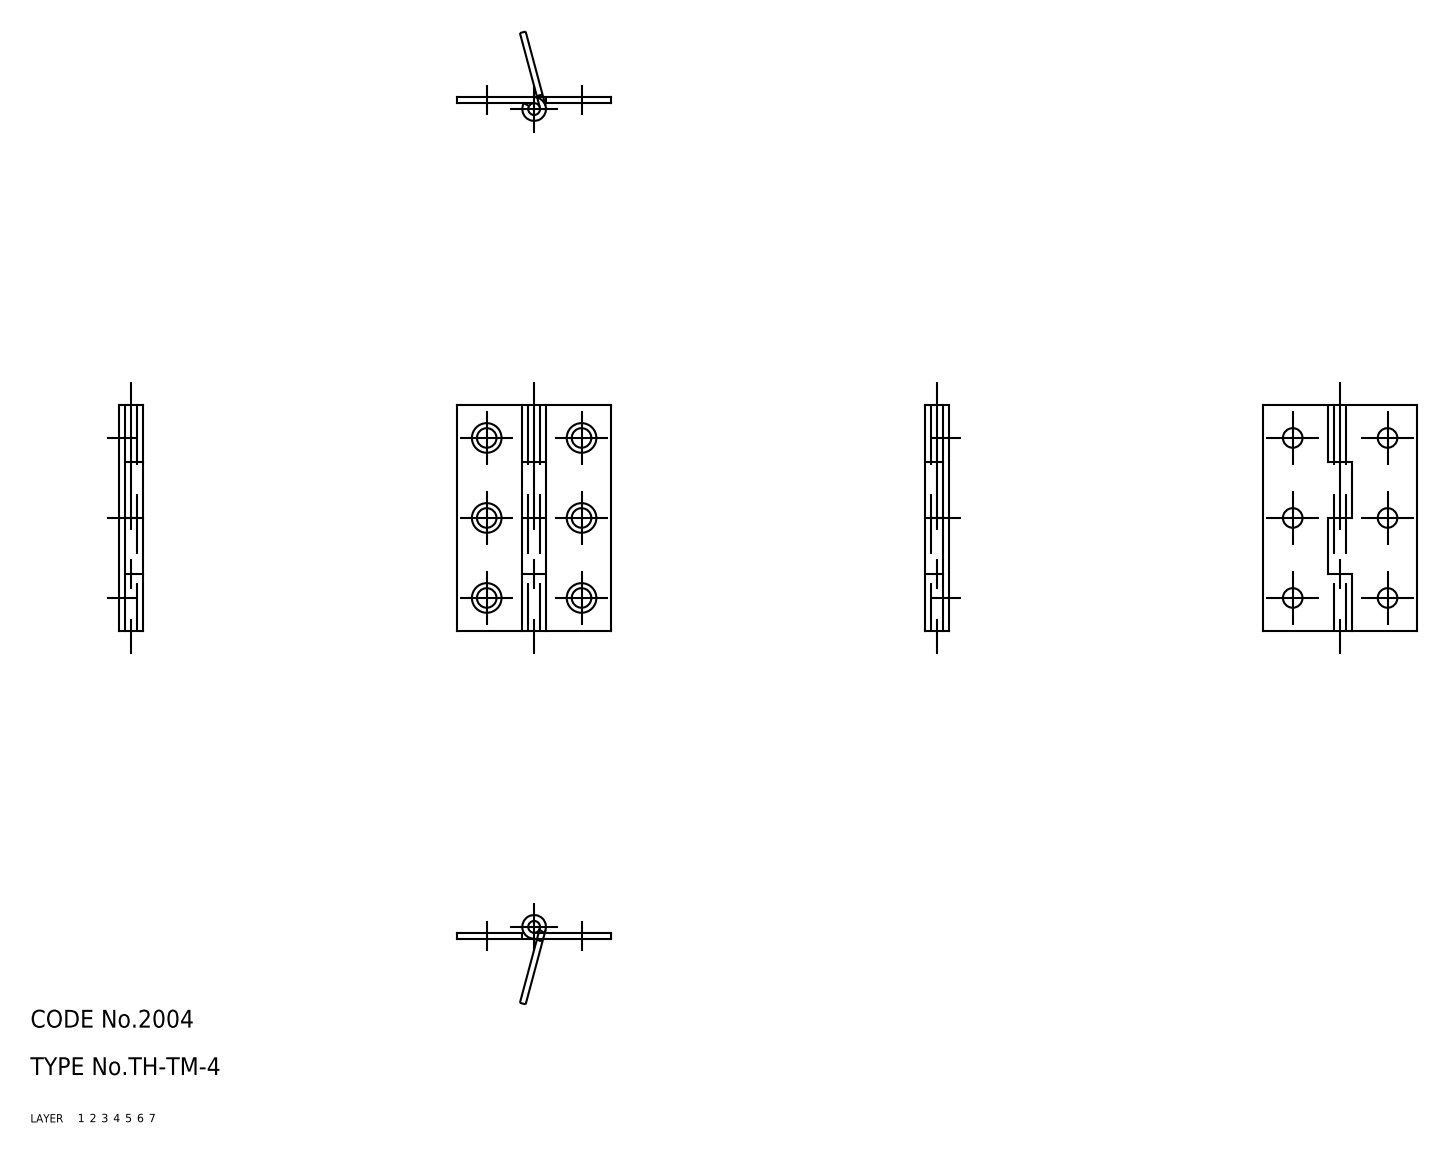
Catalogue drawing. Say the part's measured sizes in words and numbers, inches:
The part is named "shaft; hinge piece_B; hinge piece_A; TH_TM_4_23159_36". Its 3-D file was written by "CADfix (AUTOMOTIVE_DESIGN)". It is 3 solids with 60 faces: 0 planar, 0 cylindrical and 60 other. Overall it measures 1.496 by 1.024 by 0.157 inches. Its volume is 0.076 cubic inches and its surface area 4.452 square inches.
